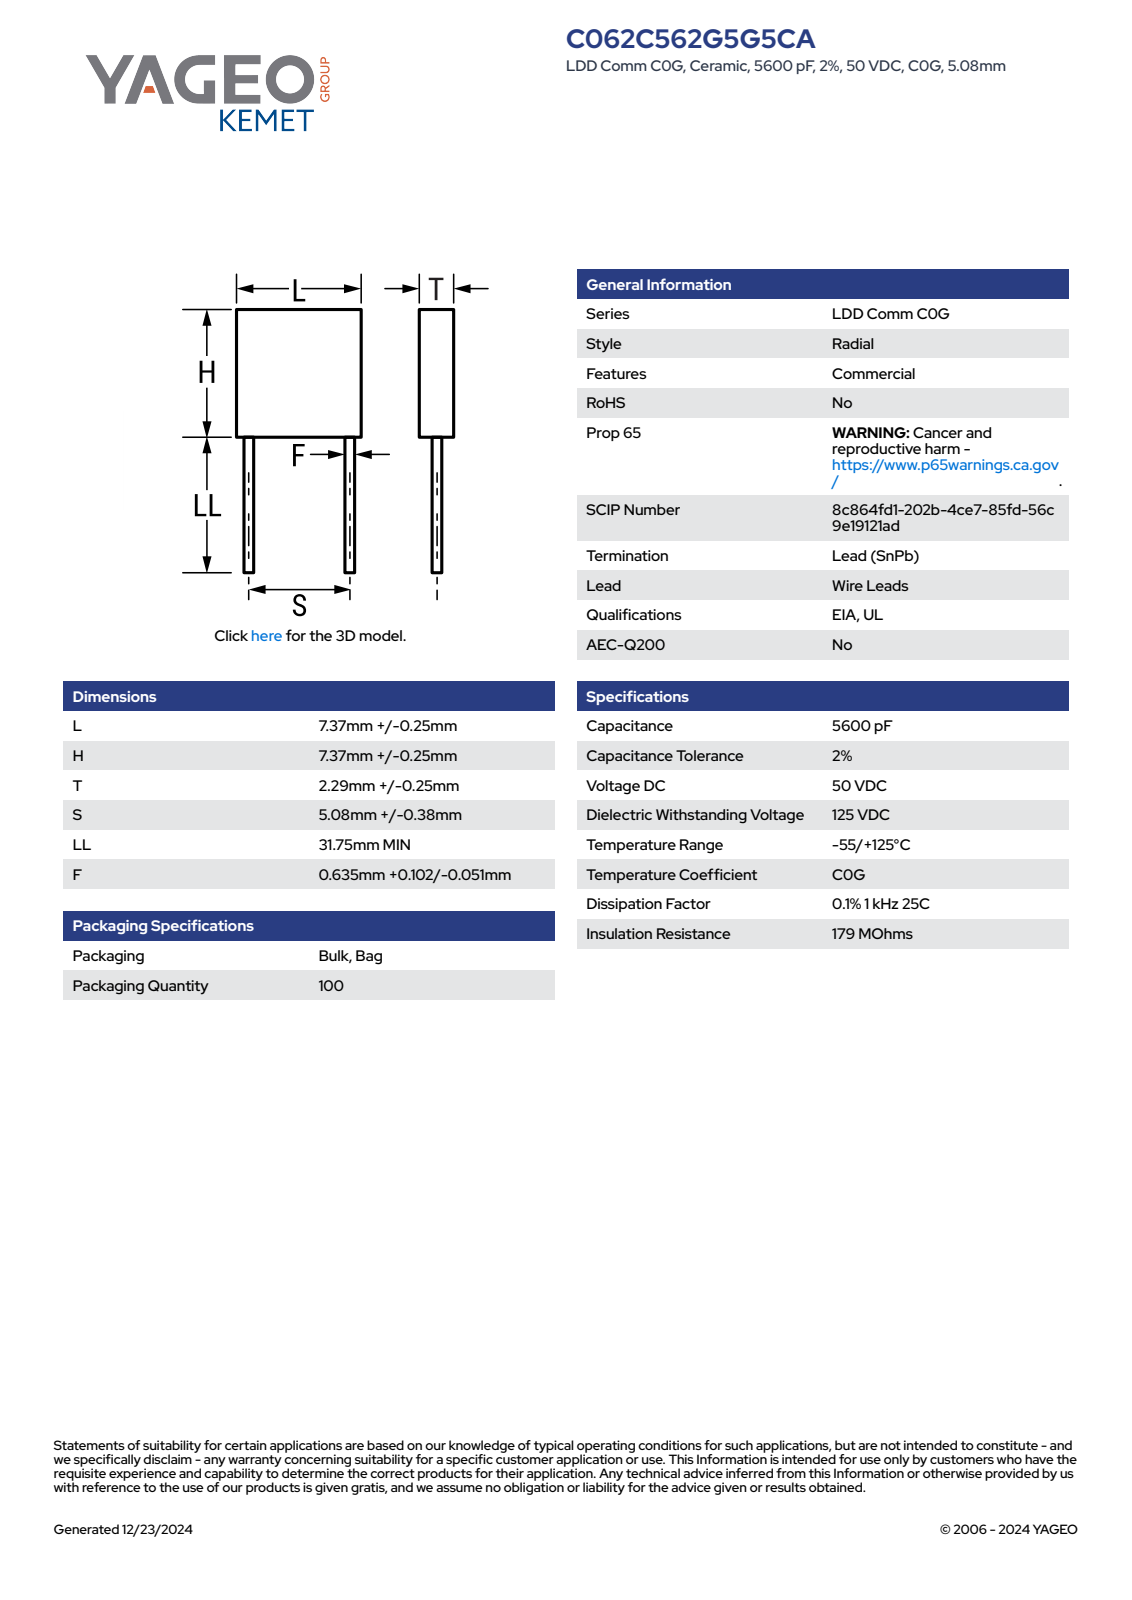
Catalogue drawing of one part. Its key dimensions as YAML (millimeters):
part_name: "CCR_RMST_C062_L7.62H7.62T2.54S5.46LL31.75F0.735"
step_written_by: "SolidWorks 2014 (AUTOMOTIVE_DESIGN)"
units: millimeters
bodies: {solids: 4, faces: 69, planar: 65, cylindrical: 4, other: 0}
overall_size: [39.37, 7.62, 2.54]
volume: 174
surface_area: 349
round_bosses_or_shafts:
  - {diameter: 0.73, count: 2}
face_to_face_distances: [2.54, 7.62, 31.75, 39.37, 36.2, 4.45, 3.17, 34.99, 3.24, 1.21]
